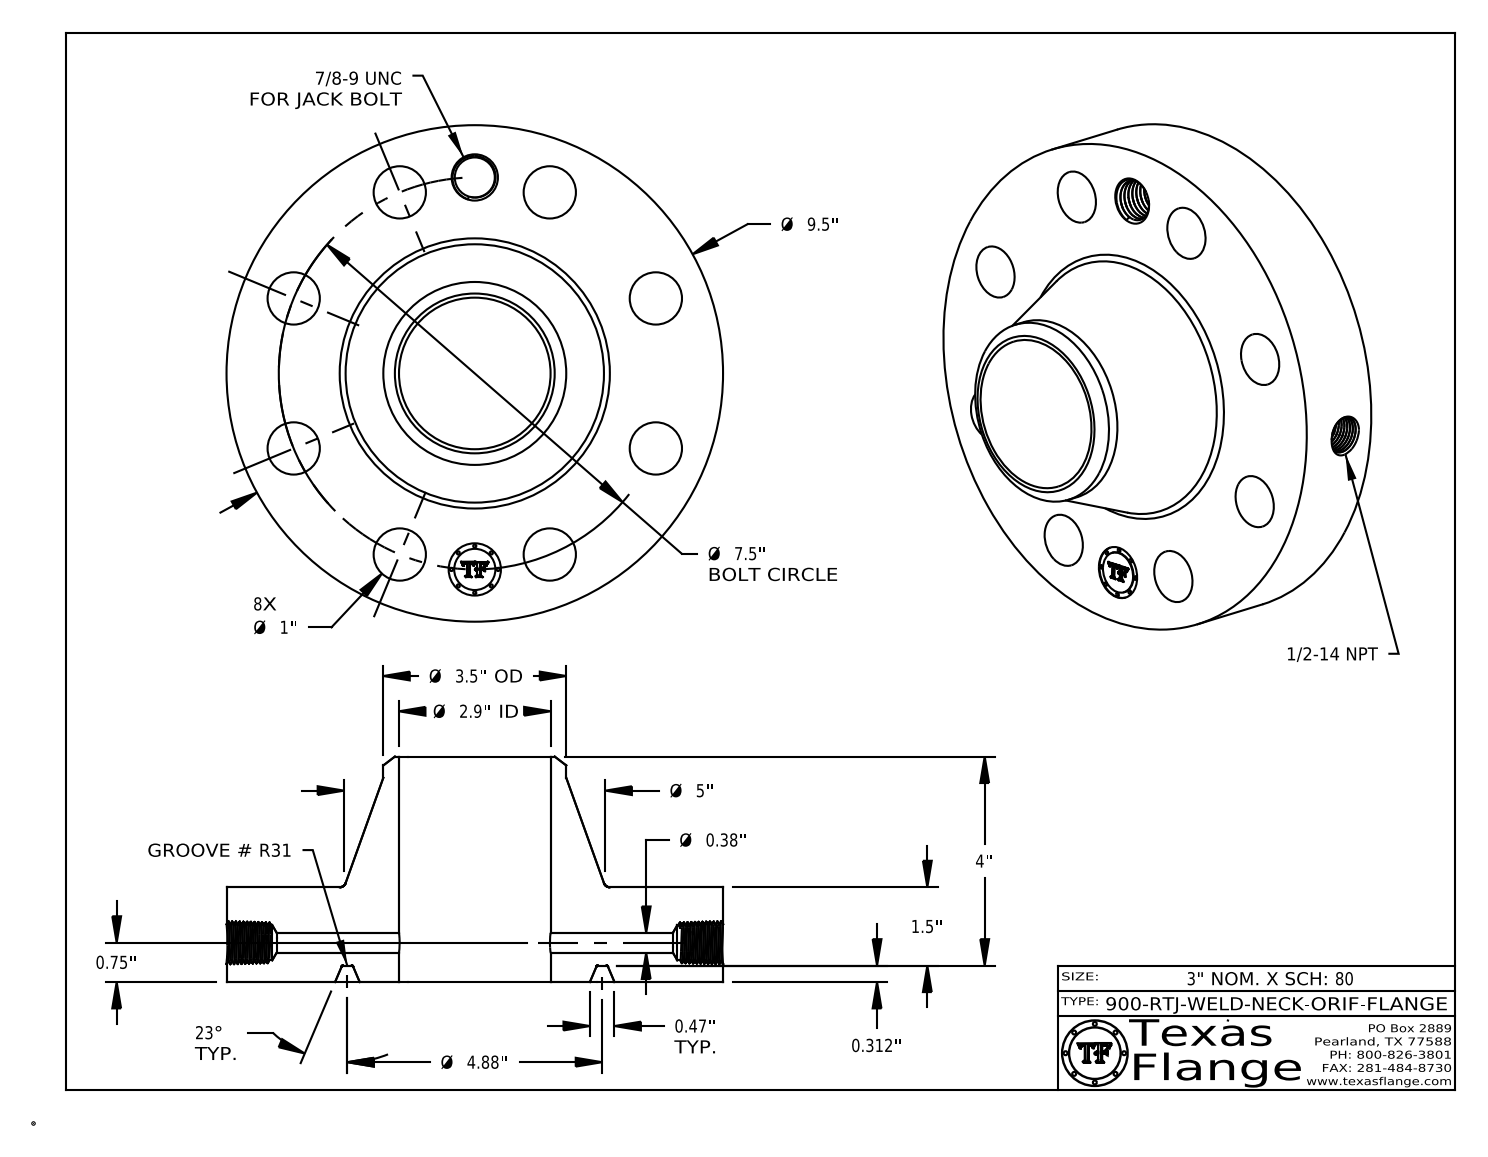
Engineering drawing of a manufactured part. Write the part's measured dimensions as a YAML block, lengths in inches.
part_name: "900-RTJ-WELD-NECK"
step_written_by: "CATIA V5 STEP AP214 (AUTOMOTIVE_DESIGN)"
units: inches
bodies: {solids: 1, faces: 784, planar: 370, cylindrical: 94, other: 320}
overall_size: [9.5, 9.5, 4.312]
volume: 118.5
surface_area: 301.3
round_holes:
  - {diameter: 1, count: 9}
  - {diameter: 0.375, count: 1}
  - {diameter: 0.672, count: 1}
  - {diameter: 0.766, count: 1}
  - {diameter: 2.9, count: 1}
round_bosses_or_shafts:
  - {diameter: 0.061, count: 8}
  - {diameter: 9.5, count: 1}
  - {diameter: 3.5, count: 1}
  - {diameter: 0.788, count: 1}
face_to_face_distances: [1.812, 0.312, 1.5, 4.312, 4, 2.5, 1.797, 1.485, 0.015, 2.515]
hole_center_spacings: [3.75, 2.87, 5.303, 6.929, 7.5, 1.463, 4.167, 6.236]
